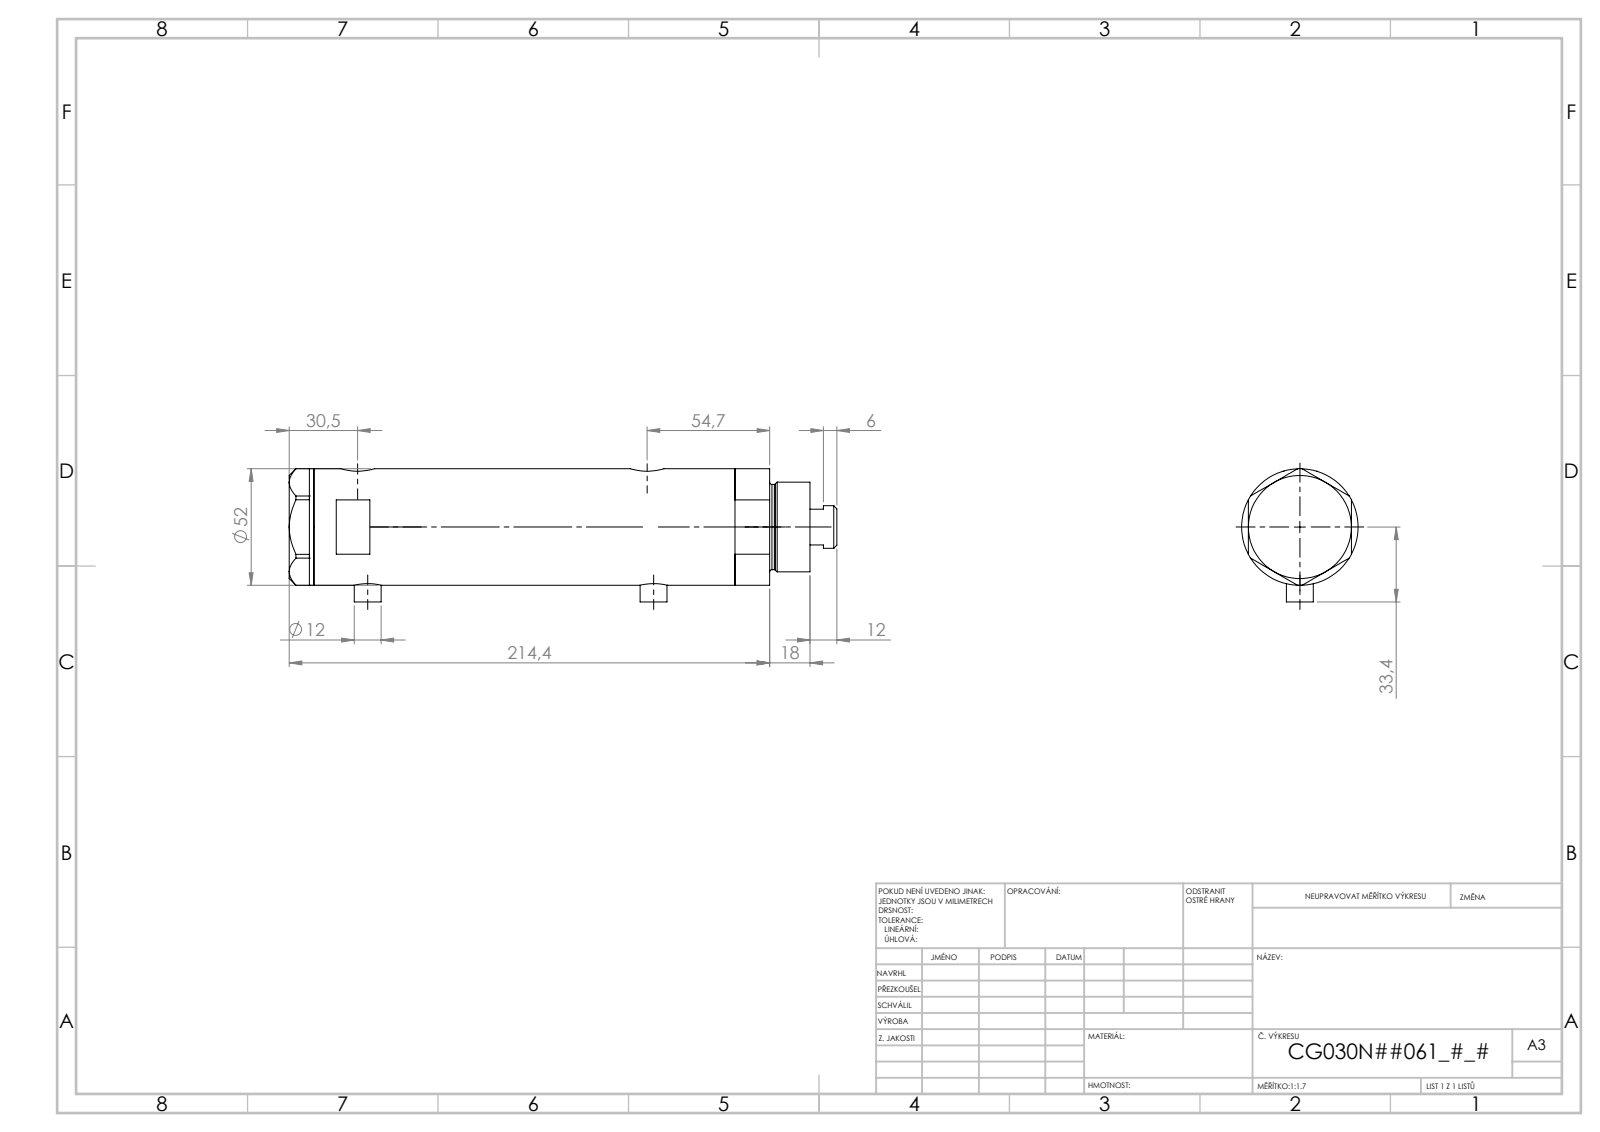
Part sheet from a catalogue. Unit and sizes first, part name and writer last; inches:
Units: inches
Overall size (bounding box): 8.269 × 2.091 × 2.047
Round holes (diameter × count): ⌀0.197 ×2, ⌀0.383 ×2, ⌀0.492 ×2, ⌀0.591 ×2, ⌀0.256 ×1, ⌀0.787 ×1, ⌀0.846 ×1, ⌀1.181 ×1, ⌀1.299 ×1, ⌀1.732 ×1
Round bosses / shafts (diameter × count): ⌀0.472 ×2, ⌀2.047 ×1, ⌀1.575 ×1, ⌀1.496 ×1, ⌀0.748 ×1
Main face-to-face distances: 0.937, 4.943, 1.811, 0.433, 0.433, 4.51, 4.509, 6.376, 5.943, 5.943
Hole centre spacings: 0.114, 0.177, 3.455, 3.569, 3.632, 3.746, 0.114, 0.115
Volume: 22.77 in³ · Surface area: 131.2 in²
Bodies: 4 solids, 140 faces (67 planar, 53 cylindrical, 20 other)
Part name (STEP PRODUCT): V270CG_MIDDLE; V270CG_VC; V270CG_BACK; V270CG_FRONT
STEP written by: SolidWorks 2019 (CONFIG_CONTROL_DESIGN)
